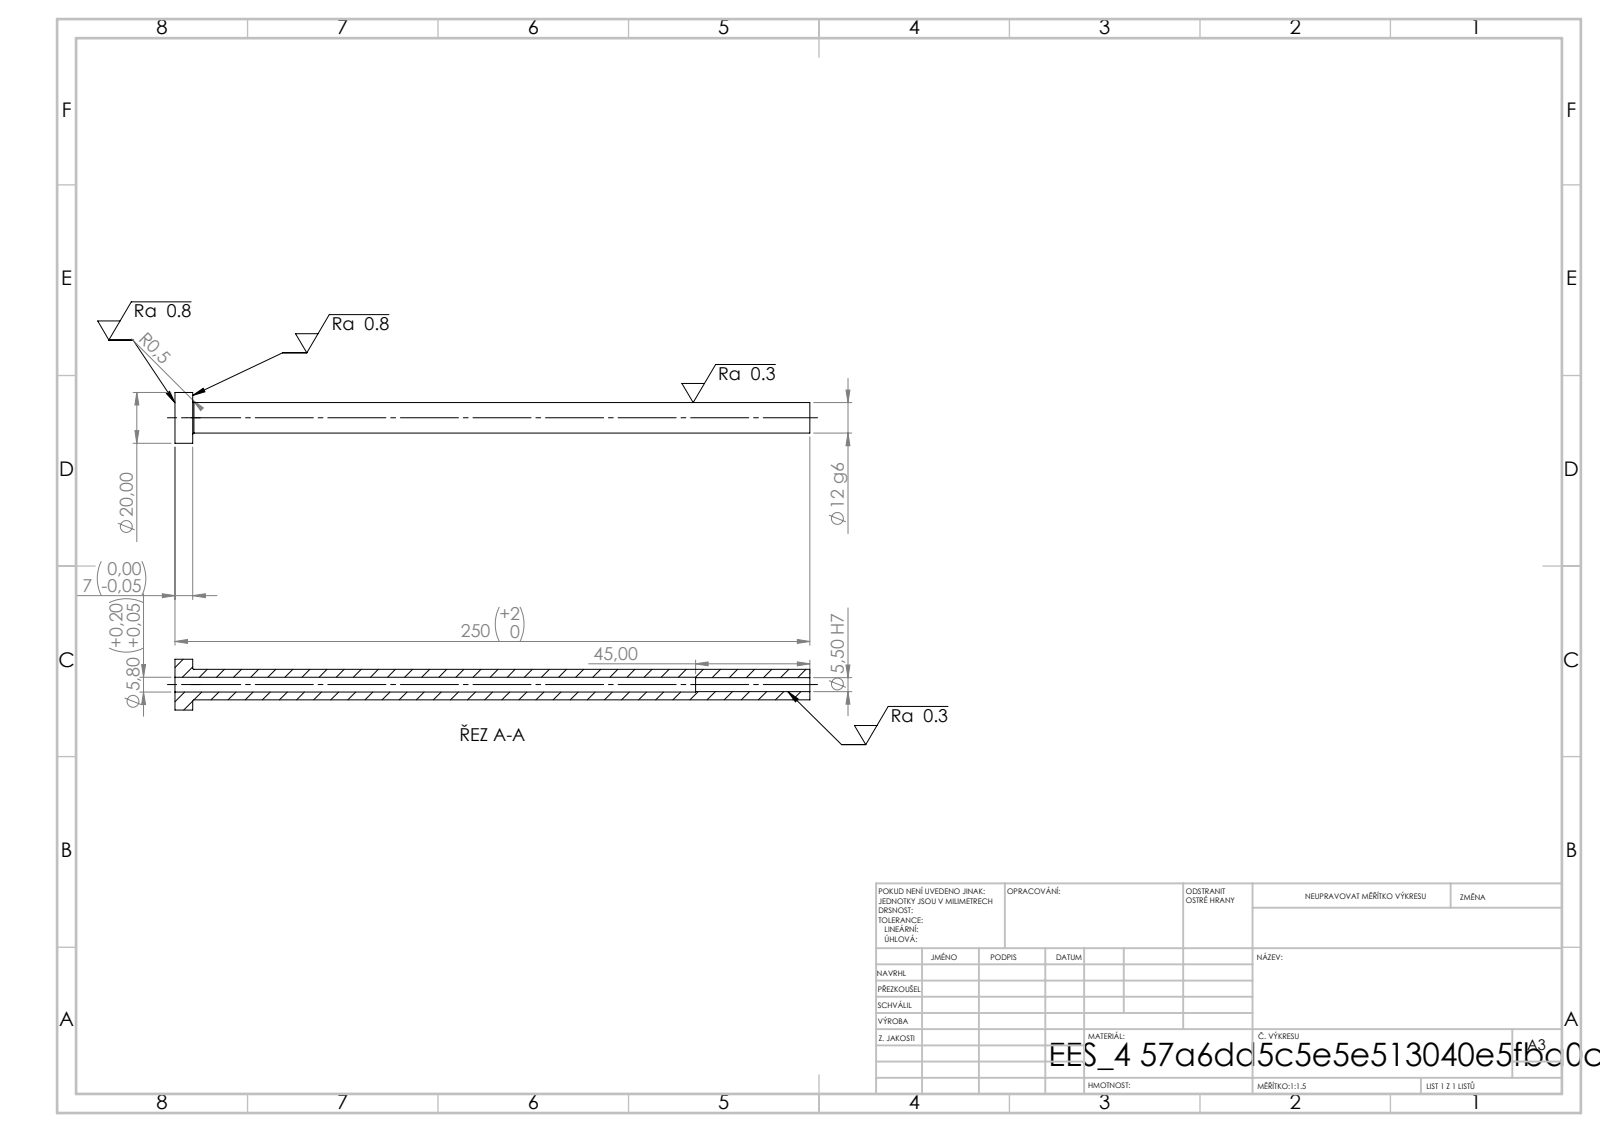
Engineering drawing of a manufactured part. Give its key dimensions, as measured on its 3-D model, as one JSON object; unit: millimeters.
{"step_written_by": "SolidWorks 2019 (CONFIG_CONTROL_DESIGN)", "units": "millimeters", "bodies": {"solids": 1, "faces": 14, "planar": 4, "cylindrical": 8, "other": 2}, "overall_size": [250, 20, 20], "volume_mm3": 23198, "surface_area_mm2": 14686, "round_holes": [[5.5, 1], [5.8, 1]], "round_bosses_or_shafts": [[20, 1], [12, 1]], "face_to_face_distances": [7, 250, 243, 205, 198, 45]}
